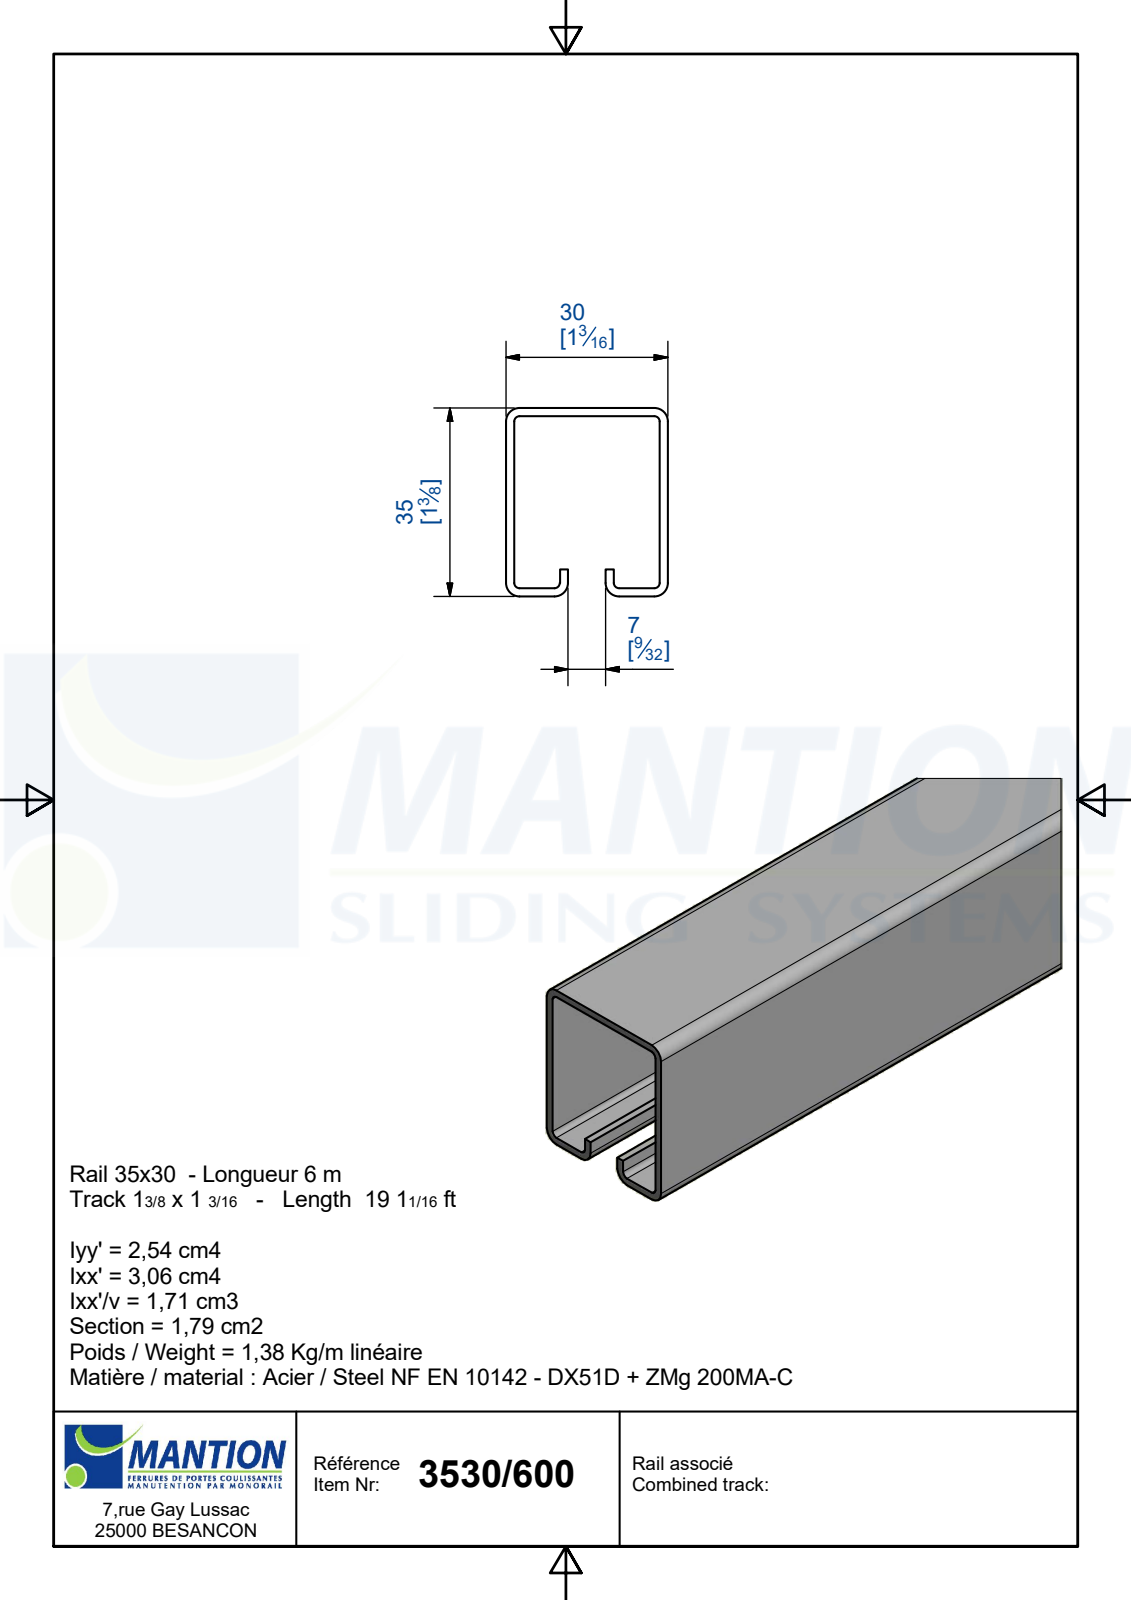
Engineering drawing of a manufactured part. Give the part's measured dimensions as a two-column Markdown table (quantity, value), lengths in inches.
| quantity | value |
| --- | --- |
| part name | 3530_600 |
| STEP written by | Autodesk Inventor 2011 (AUTOMOTIVE_DESIGN) |
| units | inches |
| bodies | 1 solid, 30 faces (18 planar, 12 cylindrical, 0 other) |
| overall size | 236.22 × 1.378 × 1.181 |
| volume | 65.6 in³ |
| surface area | 2 251 in² |
| partial cylindrical surfaces (radius × count) | 0.039 × 6, 0.098 × 6 |
| main face-to-face distances | 0.059, 1.122, 1.181, 1.063, 1.319, 1.26, 1.378, 0.394, 0.728, 0.335 |
